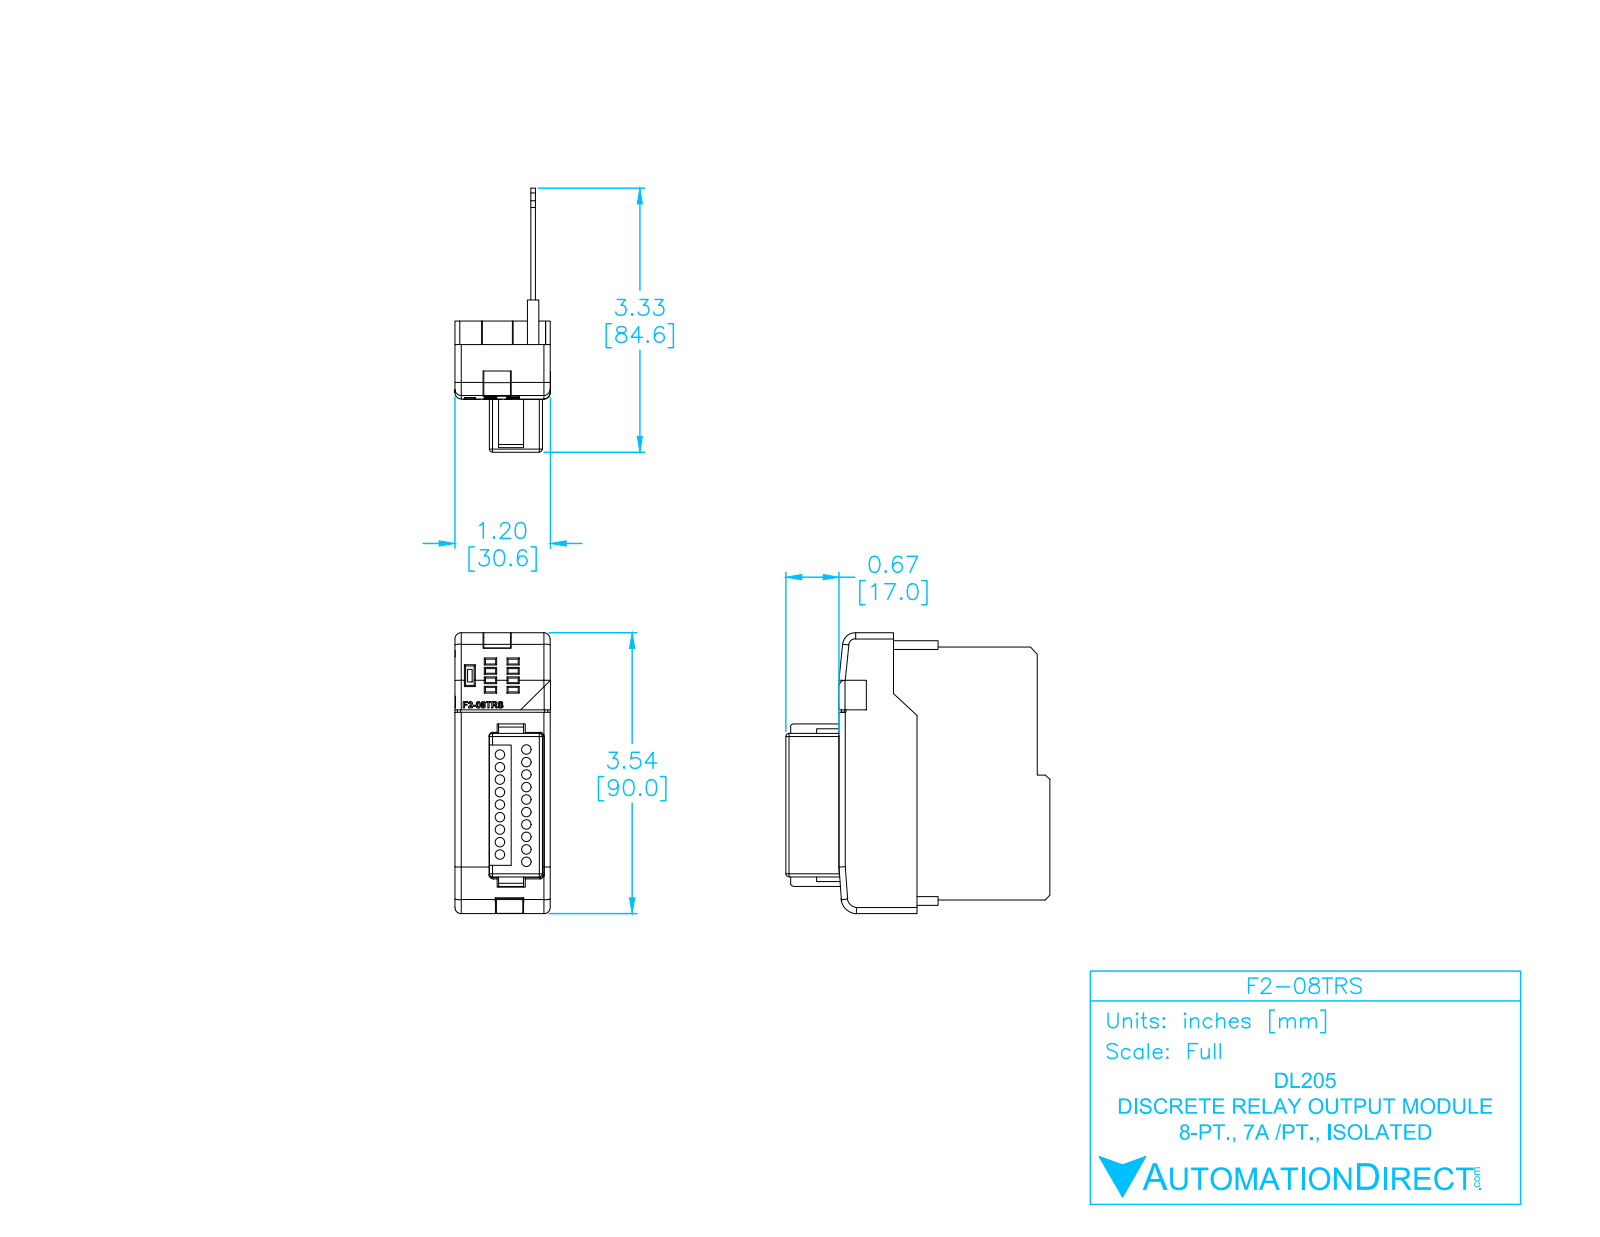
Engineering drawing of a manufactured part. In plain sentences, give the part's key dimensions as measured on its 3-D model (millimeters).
The part is named "F2-08TRS_ModuleCase Light_NEW". Its 3-D file was written by "SolidWorks 2009 (AUTOMOTIVE_DESIGN)". It is 3 solids with 639 faces: 401 planar, 158 cylindrical and 80 other. Overall it measures 90 by 84.6 by 30.55 millimeters. Its volume is 30 572 cubic millimeters and its surface area 32 675 square millimeters. Round holes: 19 of diameter 3. Partial cylindrical surfaces (rounded edges, fillets, slot ends): 28 of radius 0.35, 18 of radius 1, 12 of radius 0.5, 11 of radius 2, 6 of radius 0.25, 1 of radius 2.62, 1 of radius 3.79, 1 of radius 4.12. The main face-to-face distances are 1.5, 4.72, 3.22, 0.5, 6.22, 1, 24.28, 29, 18, 11. The hole center spacings are 4, 8, 12, 16, 8.61, 8.77, 20, 10.16.
